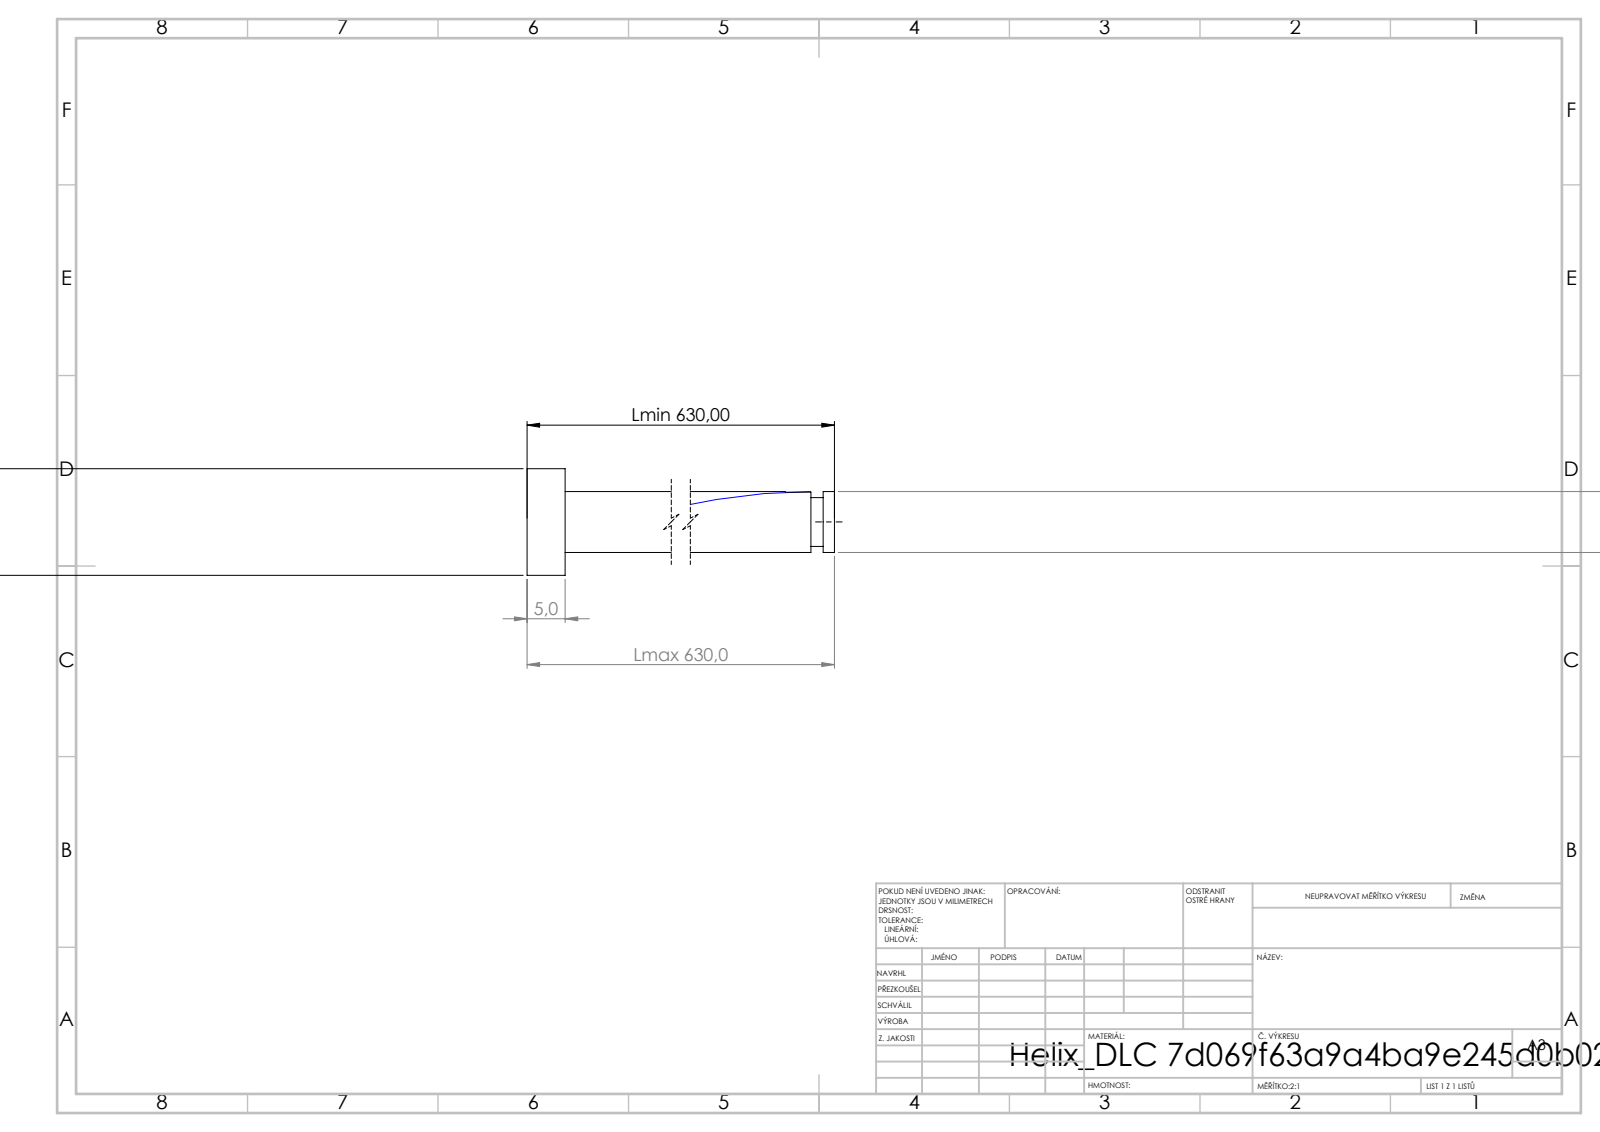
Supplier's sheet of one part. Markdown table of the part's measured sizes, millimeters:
| quantity | value |
| --- | --- |
| STEP written by | SolidWorks 2019 (CONFIG_CONTROL_DESIGN) |
| units | millimeters |
| bodies | 1 solid, 16 faces (6 planar, 9 cylindrical, 1 other) |
| overall size | 630 × 14 × 14 |
| volume | 38 890 mm³ |
| surface area | 21 787 mm² |
| round bosses / shafts (diameter × count) | 14 × 1, 8 × 1, 6.4 × 1 |
| main face-to-face distances | 5, 630, 625, 628.51, 623.51, 1.49, 626.91, 621.91, 1.6, 3.09 |
